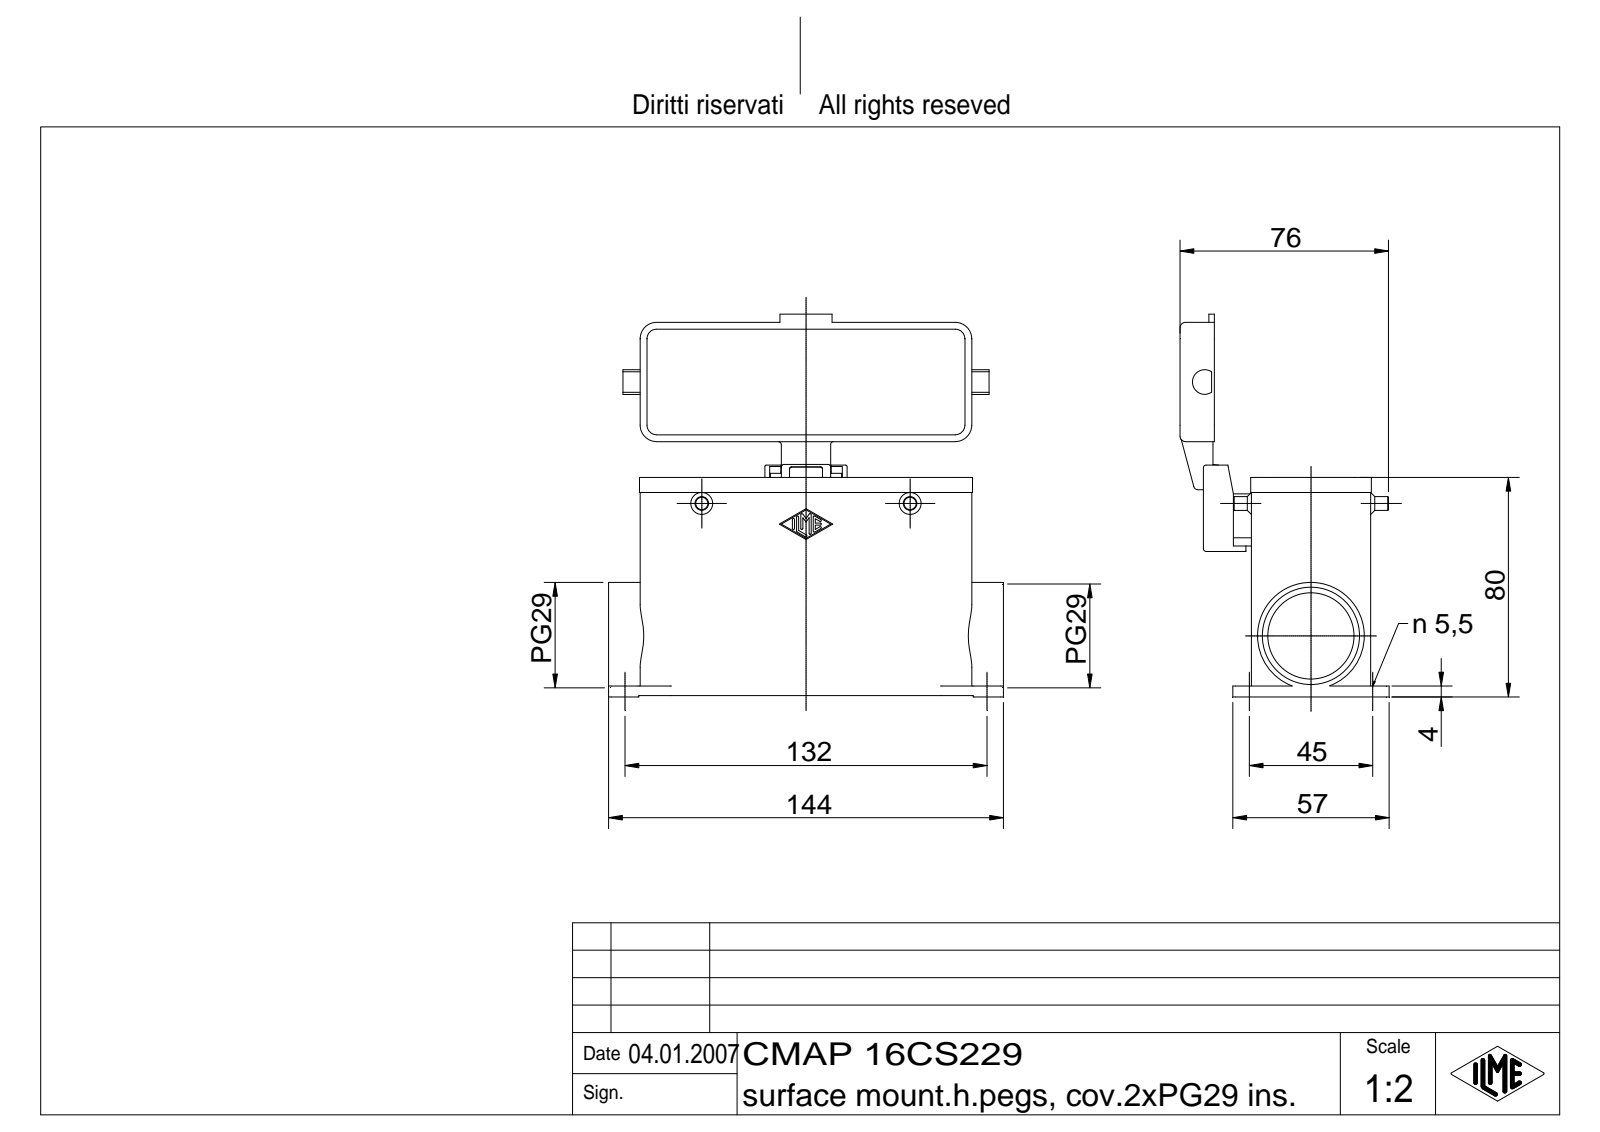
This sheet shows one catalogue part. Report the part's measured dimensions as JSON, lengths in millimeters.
{"part_name": "CMAP 16CS229", "step_written_by": "Autodesk Inventor 7 (AUTOMOTIVE_DESIGN)", "units": "millimeters", "bodies": {"solids": 2, "faces": 478, "planar": 179, "cylindrical": 179, "other": 120}, "overall_size": [144, 139.5, 76.25], "volume_mm3": 151716, "surface_area_mm2": 89252, "round_holes": [[5.5, 4], [4, 1], [5, 1], [31.48, 1], [35.48, 1]], "round_bosses_or_shafts": [[5, 2], [3, 2], [38.98, 1], [7, 1], [4, 1]], "partial_cylinders_radius": [[1, 26], [0.38, 14], [6, 12], [0.5, 9], [0.7, 8], [2, 8], [3, 4], [3.5, 4]], "face_to_face_distances": [3, 40.5, 3.5, 43.5, 37.5, 69.5, 66.5, 22.5, 29, 26], "hole_center_spacings": [45, 132, 139.46]}
